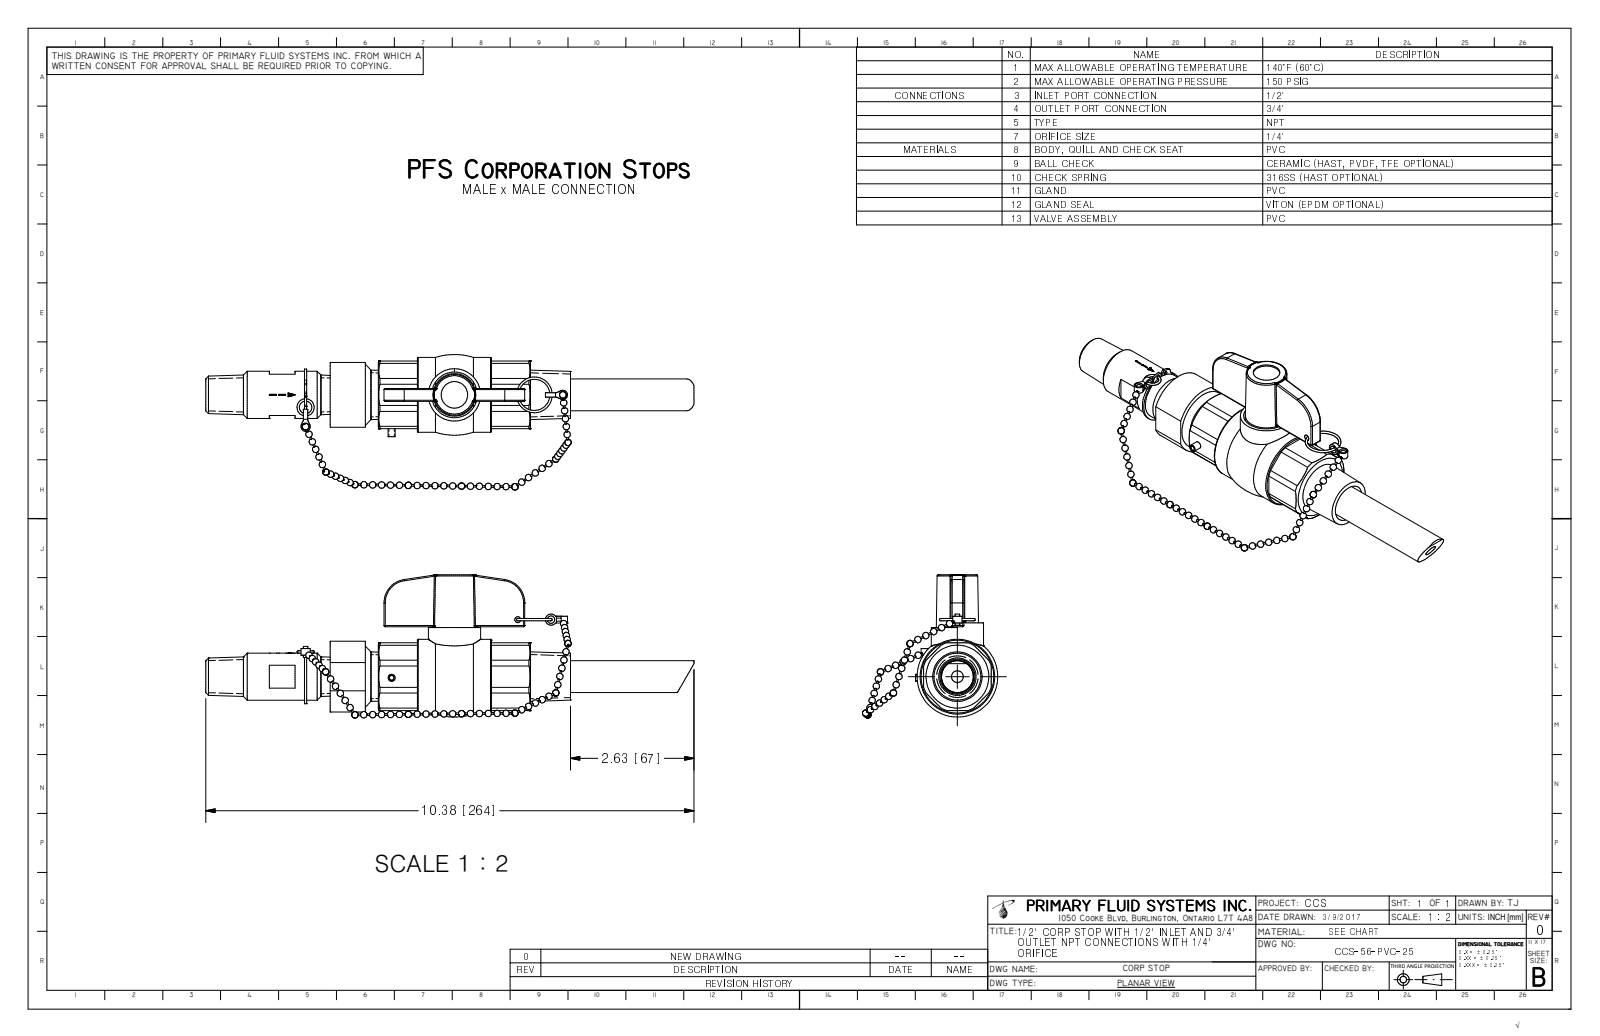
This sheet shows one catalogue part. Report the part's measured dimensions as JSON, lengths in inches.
{"part_name": "CCS-56-PVC-25_R0", "step_written_by": "Autodesk Inventor 2009 (AUTOMOTIVE_DESIGN)", "units": "inches", "bodies": {"solids": 1, "faces": 382, "planar": 115, "cylindrical": 59, "other": 208}, "overall_size": [10.38, 3.038, 2.874], "volume_in3": 12.07, "surface_area_in2": 65.16, "round_holes": [[0.079, 1], [0.15, 1], [0.25, 1], [0.469, 1], [0.56, 1], [0.563, 1], [0.97, 1]], "round_bosses_or_shafts": [[1.585, 1], [1.11, 1], [1.094, 1], [1, 1], [0.9, 1], [0.675, 1], [0.558, 1]], "partial_cylinders_radius": [[0.025, 12], [0.043, 2], [0.157, 2], [0.5, 2], [0.451, 1], [0.463, 1], [0.499, 1], [0.614, 1]], "face_to_face_distances": [1.435, 0.03, 0.55, 0.275, 0.825, 0.58, 0.855, 1.405, 0.25, 1.024], "hole_center_spacings": [0.535]}
